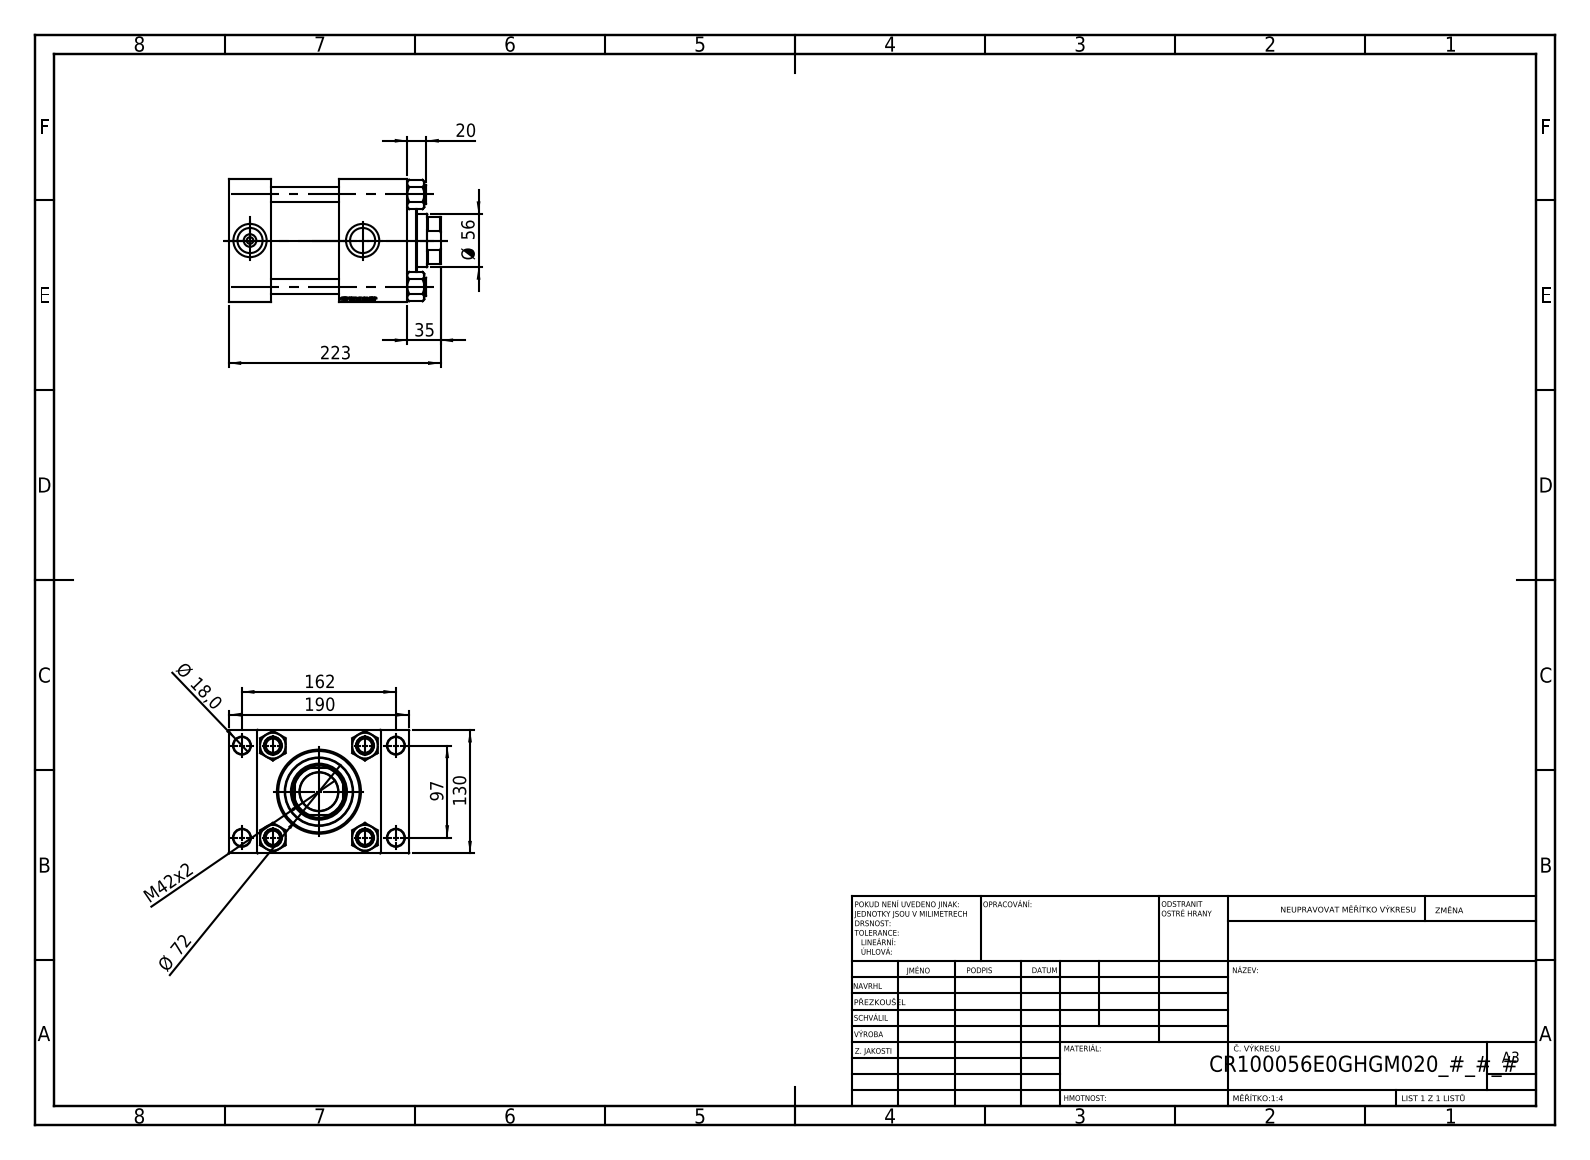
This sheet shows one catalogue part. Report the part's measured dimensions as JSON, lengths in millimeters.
{"part_name": "V215CR_TYCINKA_E; V215CR_VCP_E; V215CR_E_Body; V215_VC_A (+1 more)", "step_written_by": "SolidWorks 2019 (CONFIG_CONTROL_DESIGN)", "units": "millimeters", "bodies": {"solids": 11, "faces": 1184, "planar": 546, "cylindrical": 86, "other": 552}, "overall_size": [223, 190, 130], "volume_mm3": 2796000, "surface_area_mm2": 377104, "round_holes": [[16, 4], [18, 4], [7, 2], [26.44, 2], [35, 2], [40.5, 1], [56, 1], [59, 1], [76, 1], [85.5, 1], [100, 1]], "round_bosses_or_shafts": [[19, 4], [106, 1], [72, 1]], "partial_cylinders_radius": [[27, 1]], "face_to_face_distances": [130, 45, 188, 143, 30, 160, 116, 71, 72, 20], "hole_center_spacings": [32.55, 68.52, 94.41, 96.9, 102.27, 129.45, 161.73, 97]}
